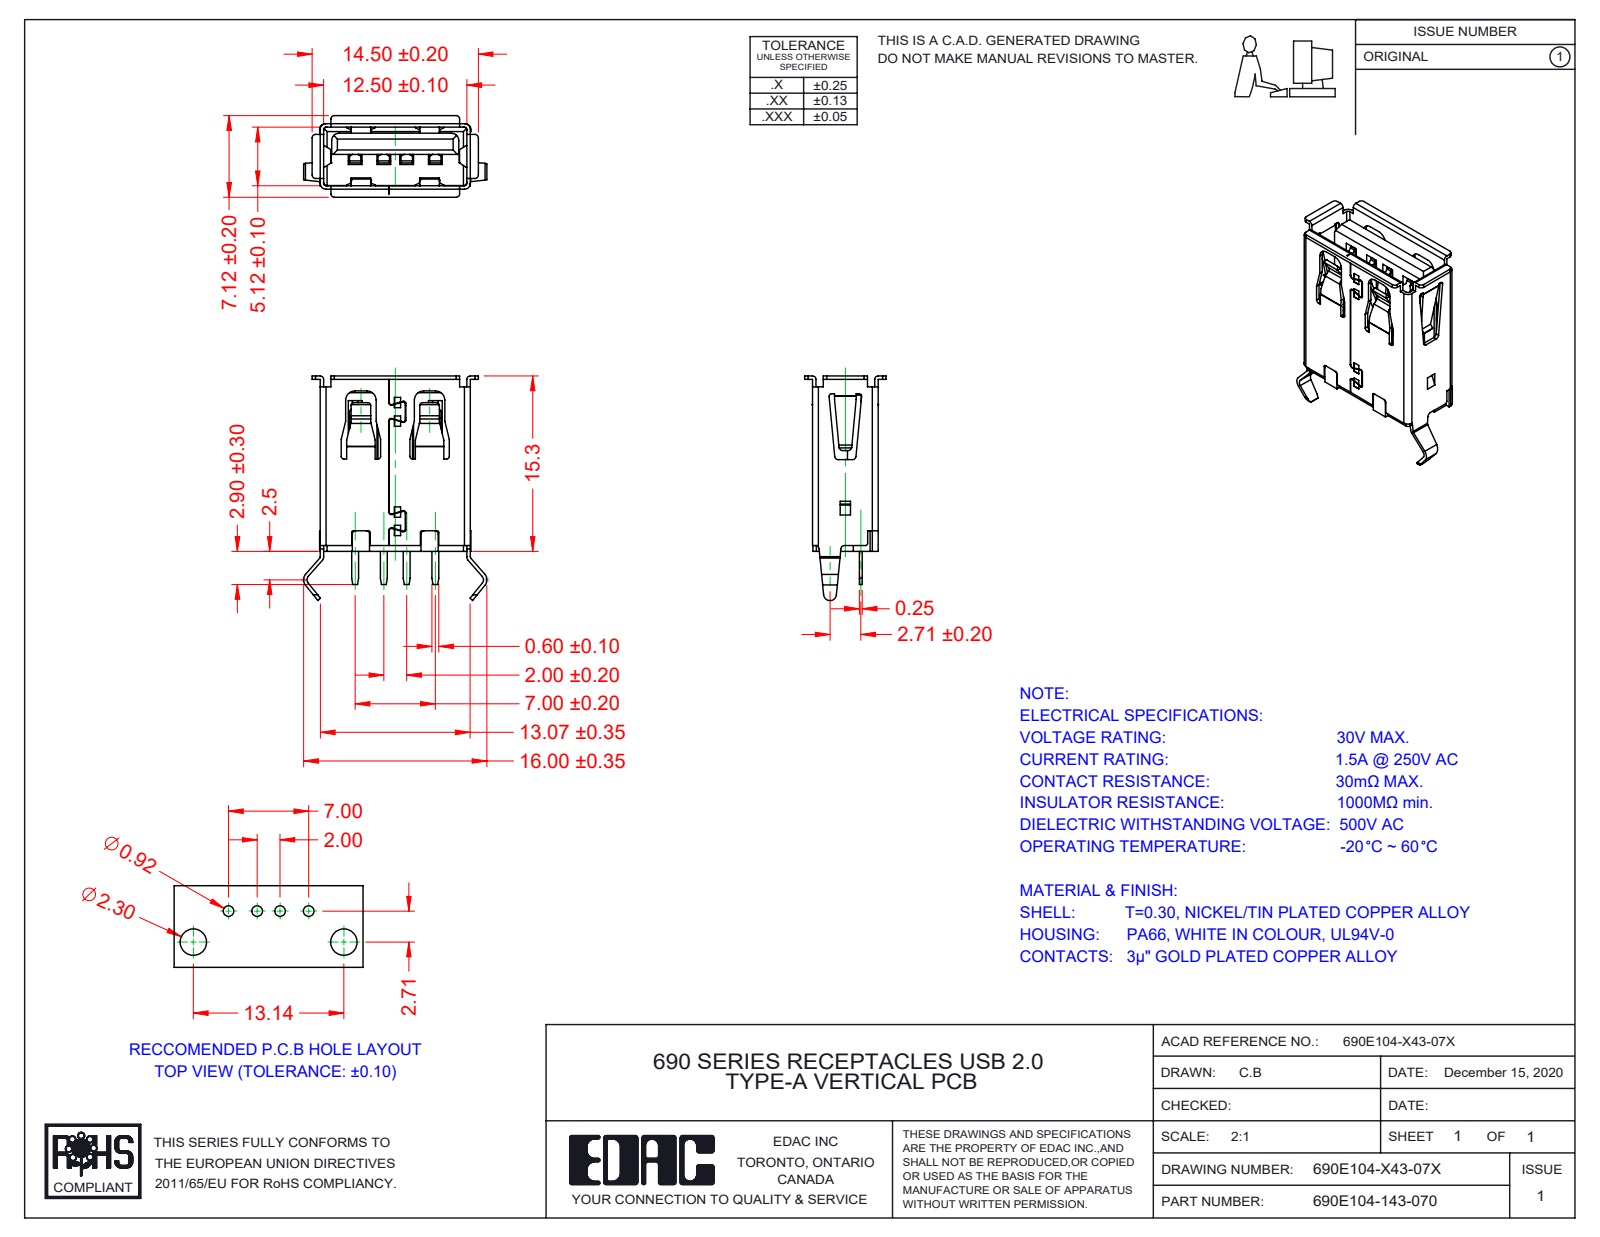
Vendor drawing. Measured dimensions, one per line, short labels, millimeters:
name: Contact 690E104-X43-07X; 690E104-143-070; Insulator2 690E104-X43-07X_White; Insulator 690E104-X43-07X_White (+1 more)
written by: SolidWorks 2020 (AUTOMOTIVE_DESIGN)
unit: mm
bodies: 7 solids, 806 faces (597 planar, 209 cylindrical, 0 other)
size: 19.6 × 16 × 7.12
volume: 609 mm³; area: 2 267 mm²
rounds: 37× R0.2, 30× R0.3, 25× R0.15, 15× R0.5, 9× R0.25, 6× R0.8, 4× R0.24, 4× R0.62
face distances: 5.42, 5.12, 5.72, 12.8, 1.09, 2.5, 1.39, 1.2, 4.5, 4.03
